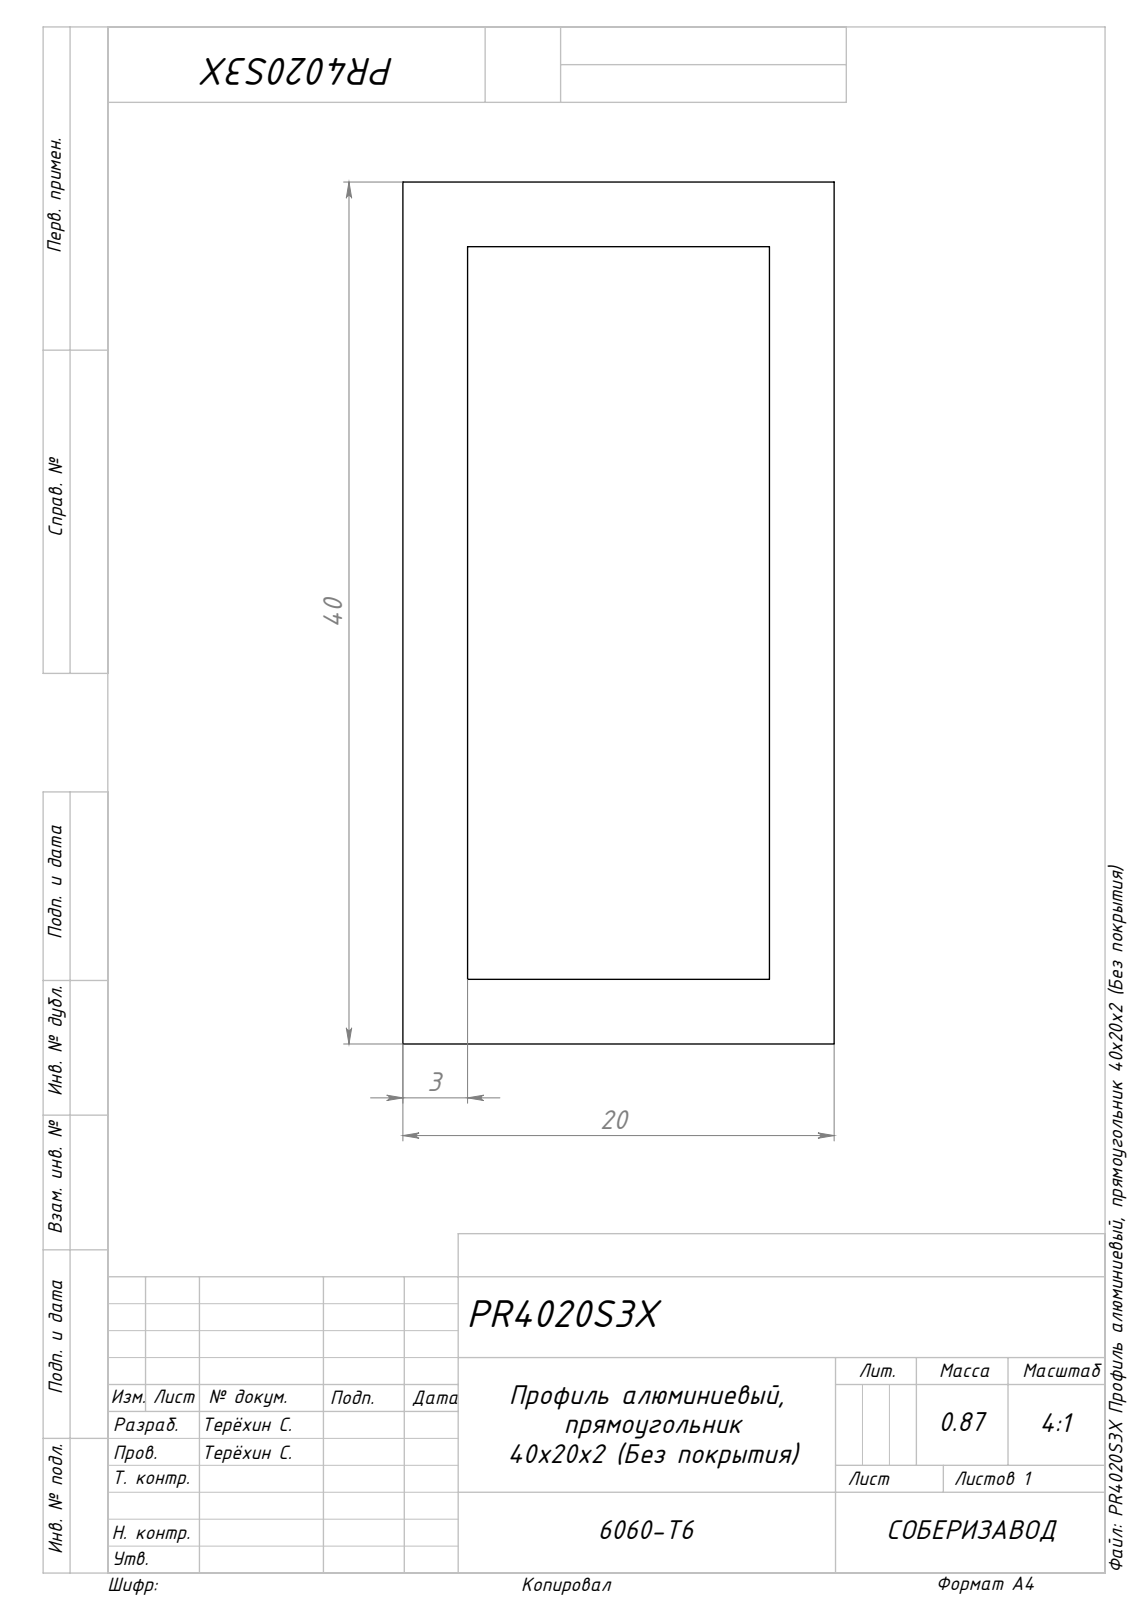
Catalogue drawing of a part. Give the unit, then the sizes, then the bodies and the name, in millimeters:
Units: millimetres
Overall size (bounding box): 1000 × 40 × 20
Main face-to-face distances: 3, 17, 20, 14, 37, 40, 34, 1000
Volume: 324 000 mm³ · Surface area: 216 648 mm²
Bodies: 1 solid, 10 faces (10 planar, 0 cylindrical, 0 other)
Part name (STEP PRODUCT): PR4020S3X Профиль алюминиевый, прямоугольник 40x20x2 (Без покрытия)
STEP written by: SolidWorks 2024 (AUTOMOTIVE_DESIGN)
